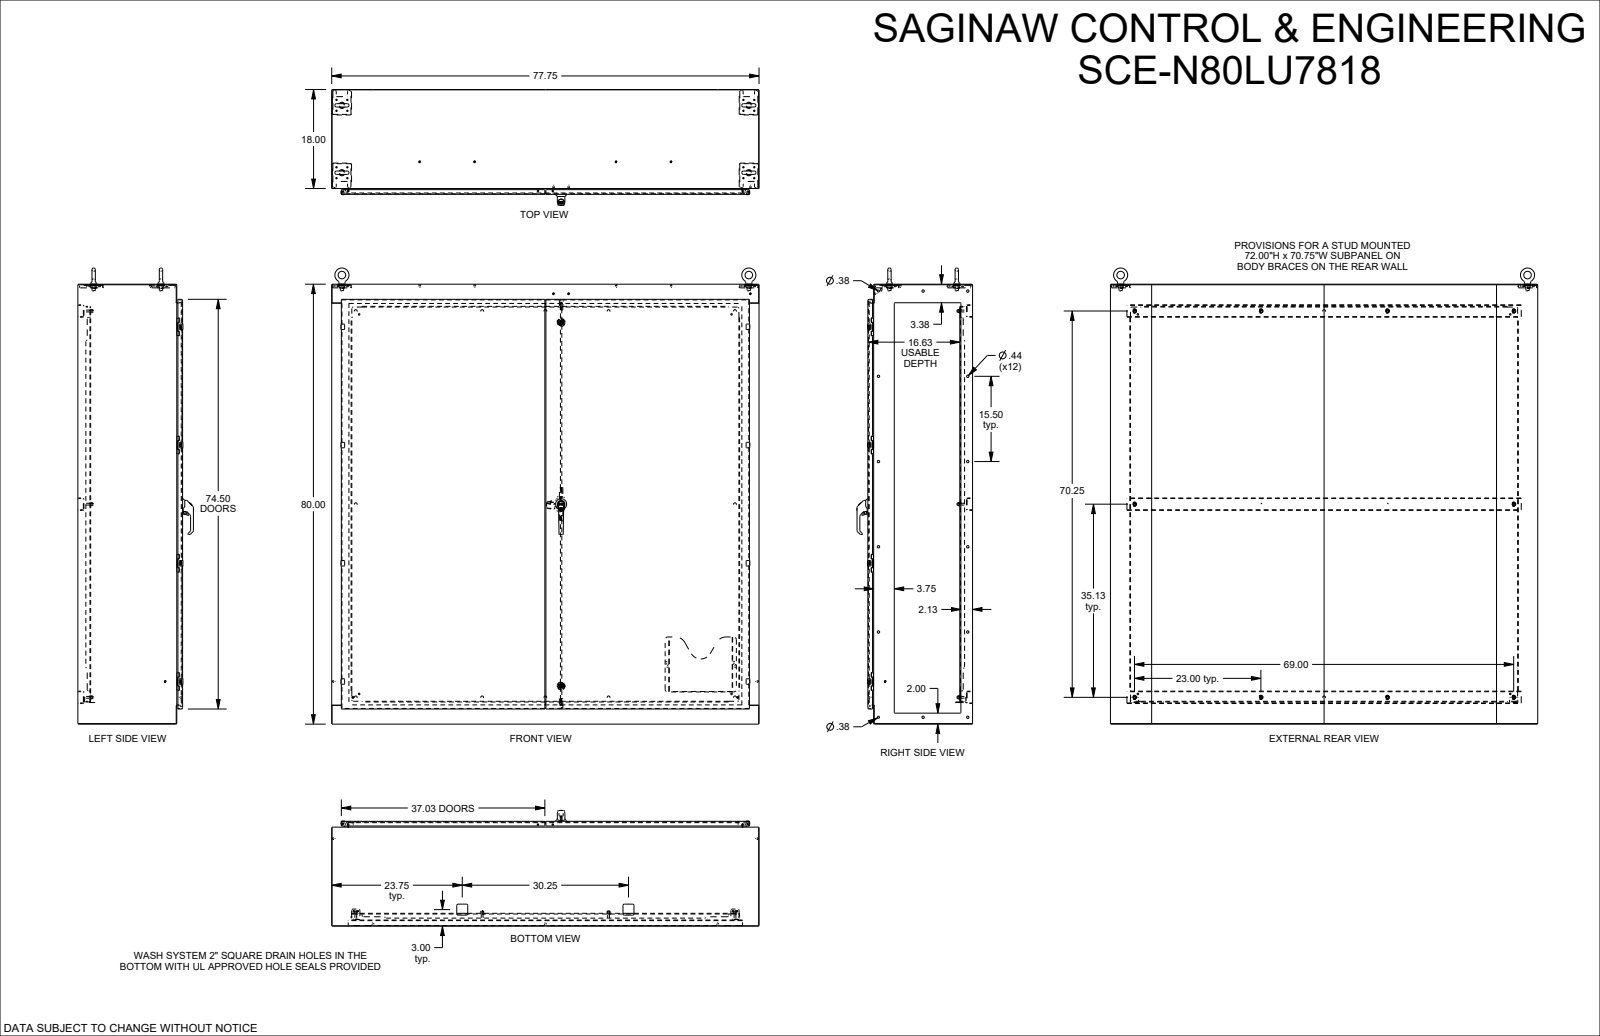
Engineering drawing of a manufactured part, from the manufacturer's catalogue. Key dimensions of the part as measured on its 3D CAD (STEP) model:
Part name (STEP PRODUCT): SCE-N80LU7818
STEP written by: SolidWorks 2023 (AUTOMOTIVE_DESIGN)
Units: inches
Bodies: 36 solids, 5131 faces (2432 planar, 1687 cylindrical, 1012 other)
Overall size (bounding box): 82.945 × 77.75 × 21.046
Volume: 2 042 in³ · Surface area: 39 167 in²
Round holes (diameter × count): ⌀0.25 ×19, ⌀0.375 ×18, ⌀0.205 ×16, ⌀0.244 ×16, ⌀0.437 ×12, ⌀0.04 ×8, ⌀0.218 ×8, ⌀0.17 ×4, ⌀0.256 ×4, ⌀0.875 ×4, ⌀0.206 ×2, ⌀0.343 ×2
Round bosses / shafts (diameter × count): ⌀0.17 ×24, ⌀0.25 ×16, ⌀0.24 ×16, ⌀0.645 ×12, ⌀0.196 ×10, ⌀1.173 ×4, ⌀0.6 ×4, ⌀1.4 ×2
Partial cylindrical surfaces — rounded edges, fillets, slot ends (radius × count): R0.03 ×102, R0.015 ×88, R0.125 ×67, R0.04 ×41, R0.167 ×38, R0.062 ×34, R0.063 ×32, R0.229 ×32
Main face-to-face distances: 0.104, 18.954, 18.85, 19.058, 79.896, 17.896, 1.058, 80, 79.792, 77.646
Hole centre spacings: 21.5, 1.979, 43, 72.868, 1.4, 75.934, 76.113, 15.5
